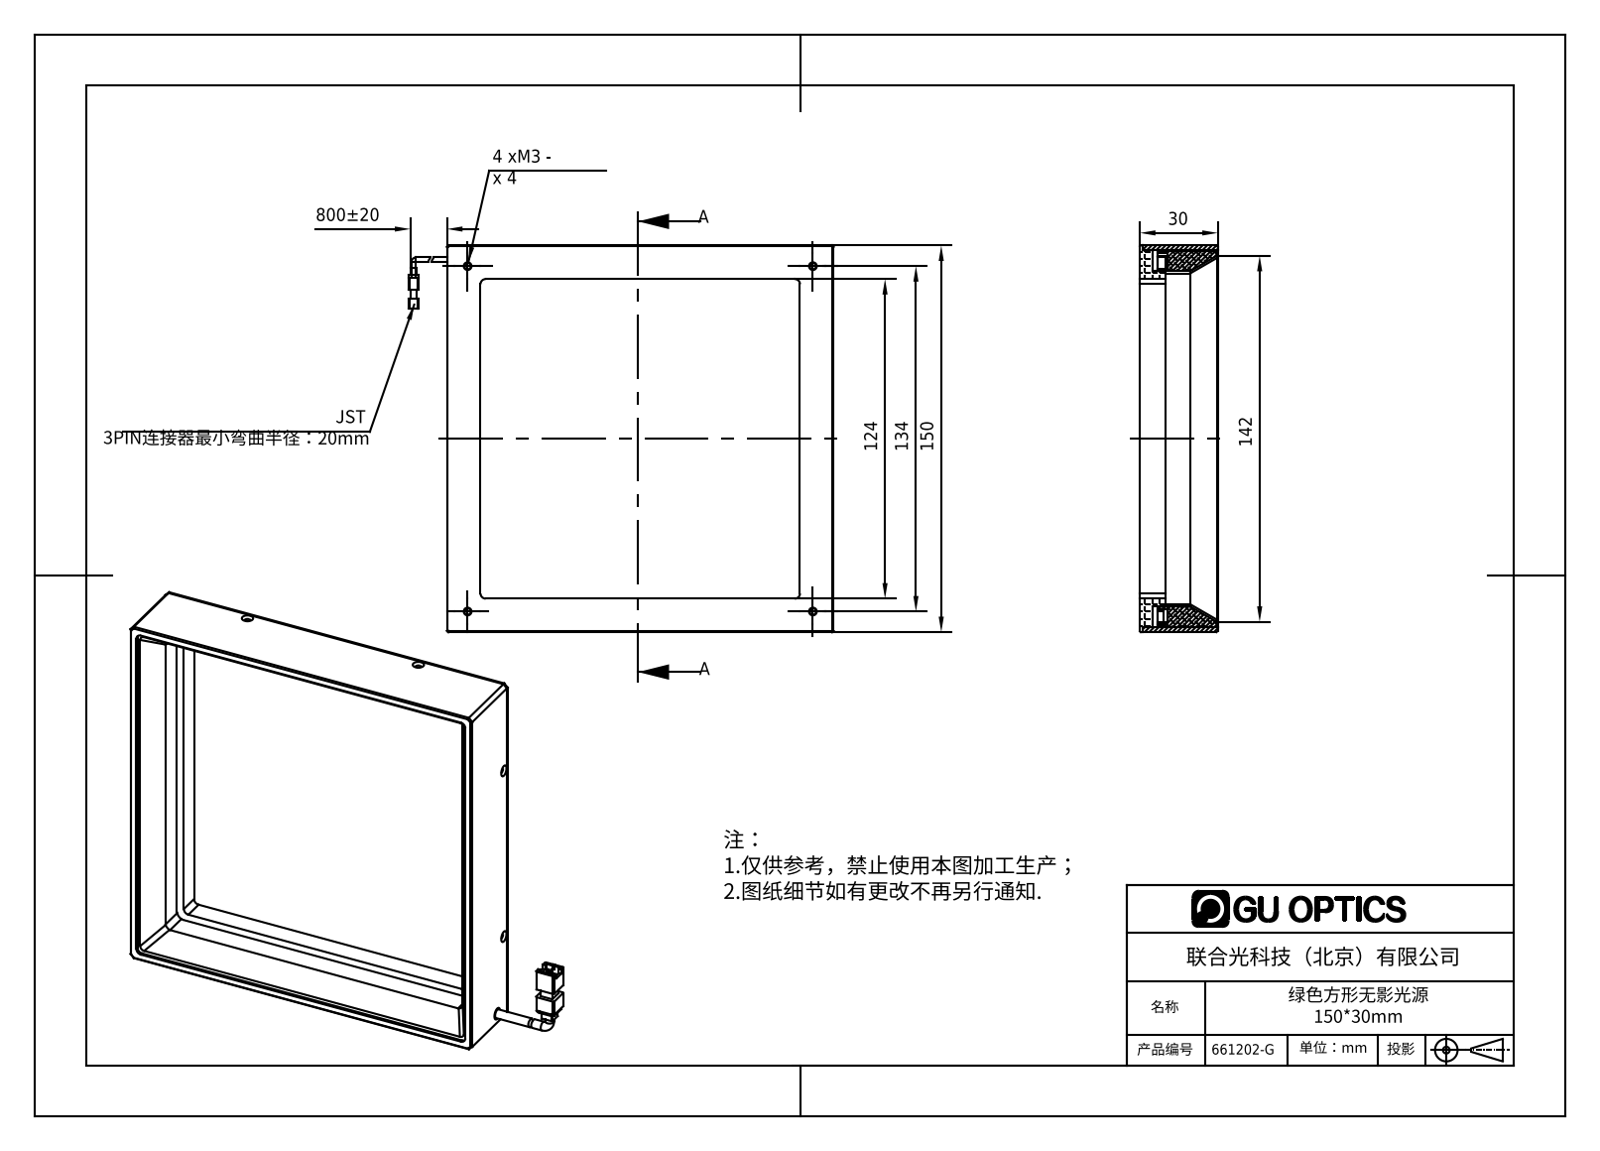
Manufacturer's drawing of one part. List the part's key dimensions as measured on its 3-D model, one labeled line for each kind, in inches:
Part name (STEP PRODUCT): 661202-G
STEP written by: SolidWorks 2016 (AUTOMOTIVE_DESIGN)
Units: inches
Bodies: 9 solids, 477 faces (245 planar, 124 cylindrical, 108 other)
Overall size (bounding box): 6.969 × 5.906 × 1.189
Volume: 8.738 in³ · Surface area: 168.2 in²
Round holes (diameter × count): ⌀0.049 ×4, ⌀0.063 ×4, ⌀0.094 ×4, ⌀0.098 ×4, ⌀0.118 ×4
Round bosses / shafts (diameter × count): ⌀0.138 ×2
Partial cylindrical surfaces — rounded edges, fillets, slot ends (radius × count): R0.079 ×18, R0.118 ×12, R0.02 ×8, R0.039 ×4
Main face-to-face distances: 0.071, 5.835, 0.039, 5.441, 0.224, 0.197, 5.764, 5.906, 0.307, 0.394
Hole centre spacings: 5.276, 2.953, 7.461
